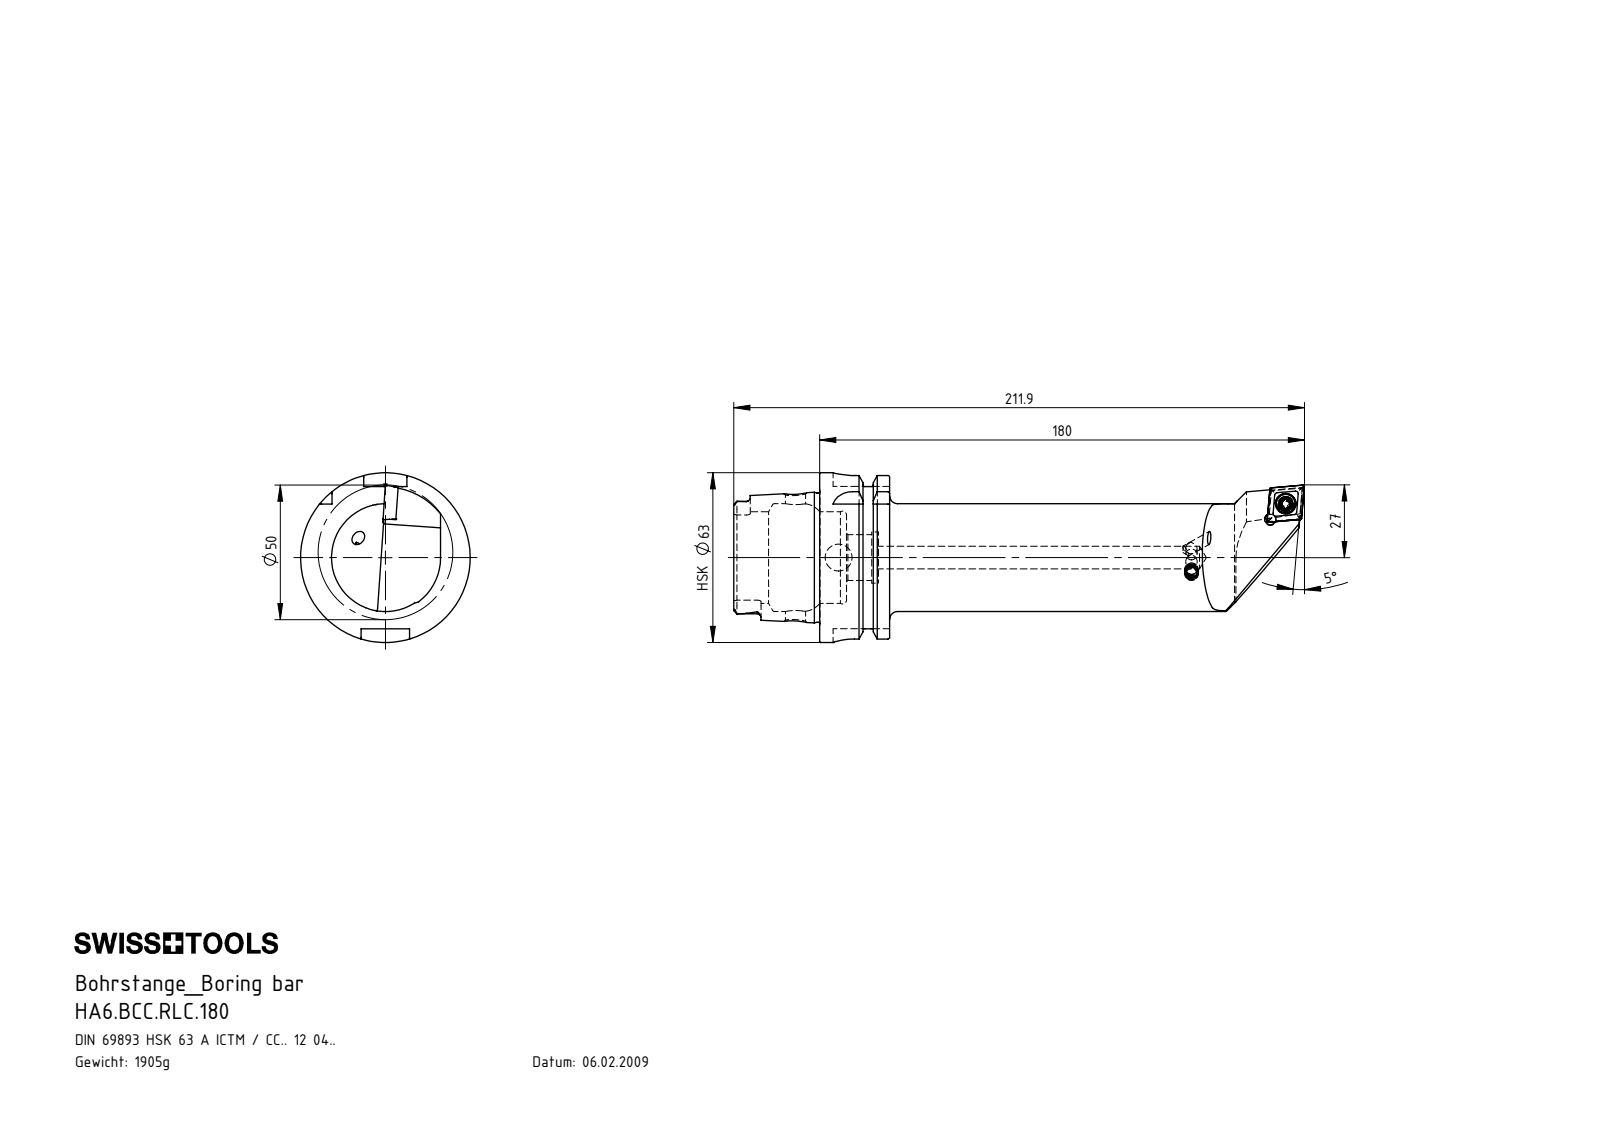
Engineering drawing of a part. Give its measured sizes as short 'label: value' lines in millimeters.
name: HA6-BCC.RLC.180; KVT_MB_600_050; WCC-ER2.001.010_A; CCMT120404 (+1 more)
written by: SolidWorks 2012 (AUTOMOTIVE_DESIGN)
unit: mm
bodies: 5 solids, 301 faces (75 planar, 88 cylindrical, 138 other)
size: 211.86 × 63 × 63
volume: 242 713 mm³; area: 44 565 mm²
holes: 4× ⌀4.2, 1× ⌀4, 1× ⌀5.5, 1× ⌀7.5, 1× ⌀7.6, 1× ⌀8.4, 1× ⌀10, 1× ⌀17, 1× ⌀19, 1× ⌀34, 1× ⌀40
bosses: 2× ⌀5, 1× ⌀63, 1× ⌀54.95, 1× ⌀47.94, 1× ⌀7
rounds: 6× R0.39, 6× R0.69, 6× R1.4, 4× R8, 2× R2.82, 2× R2.88, 1× R6, 1× R20.5
face distances: 25.95, 16, 9.95, 31.9, 41.85, 57.85, 52.8, 21.8, 11.85, 53.7
hole spacings: 8.09
